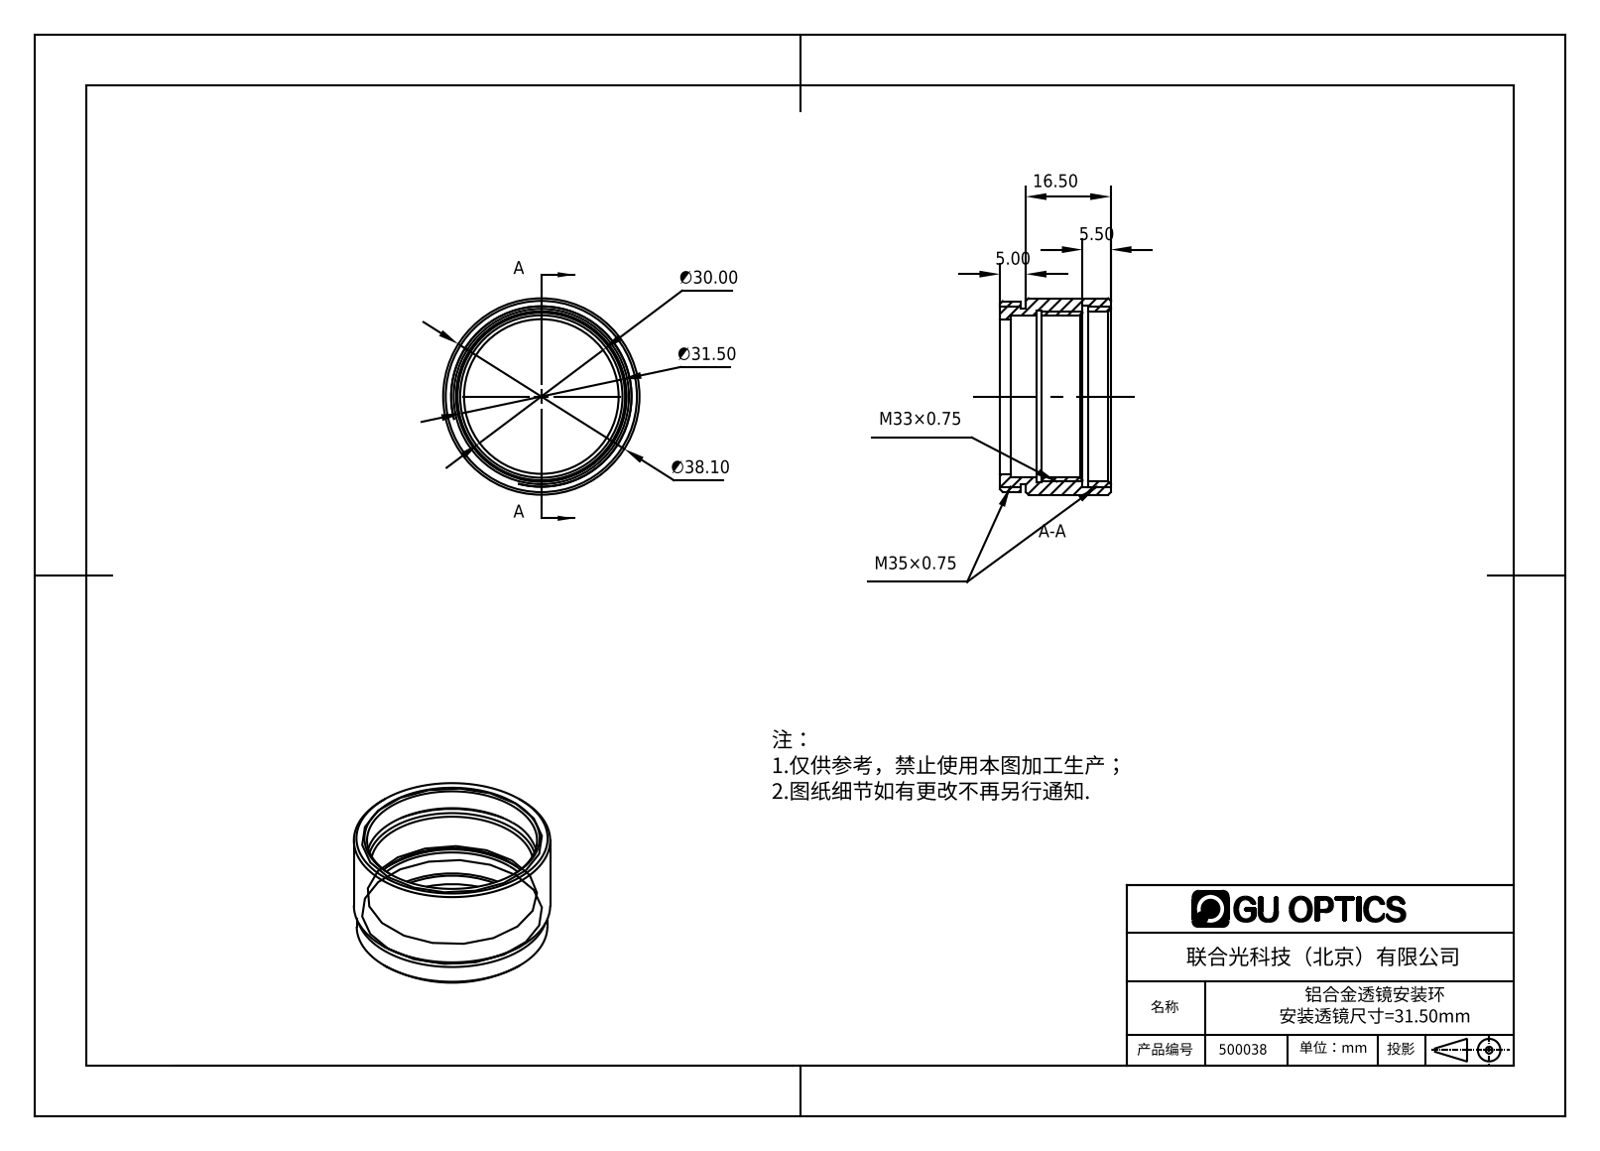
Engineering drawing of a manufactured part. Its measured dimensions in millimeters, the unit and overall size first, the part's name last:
Units: millimetres
Overall size (bounding box): 38.1 × 38.1 × 21.5
Round holes (diameter × count): ⌀30 ×1, ⌀31.5 ×1, ⌀33 ×1, ⌀33.3 ×1, ⌀35.3 ×1
Round bosses / shafts (diameter × count): ⌀38.1 ×1, ⌀37 ×1, ⌀34 ×1
Main face-to-face distances: 1, 12, 4, 3, 5, 2, 9, 8, 21.5, 16.5
Volume: 6 707 mm³ · Surface area: 6 171 mm²
Bodies: 1 solid, 37 faces (9 planar, 18 cylindrical, 10 other)
Part name (STEP PRODUCT): 500038
STEP written by: SolidWorks 2016 (AUTOMOTIVE_DESIGN)
